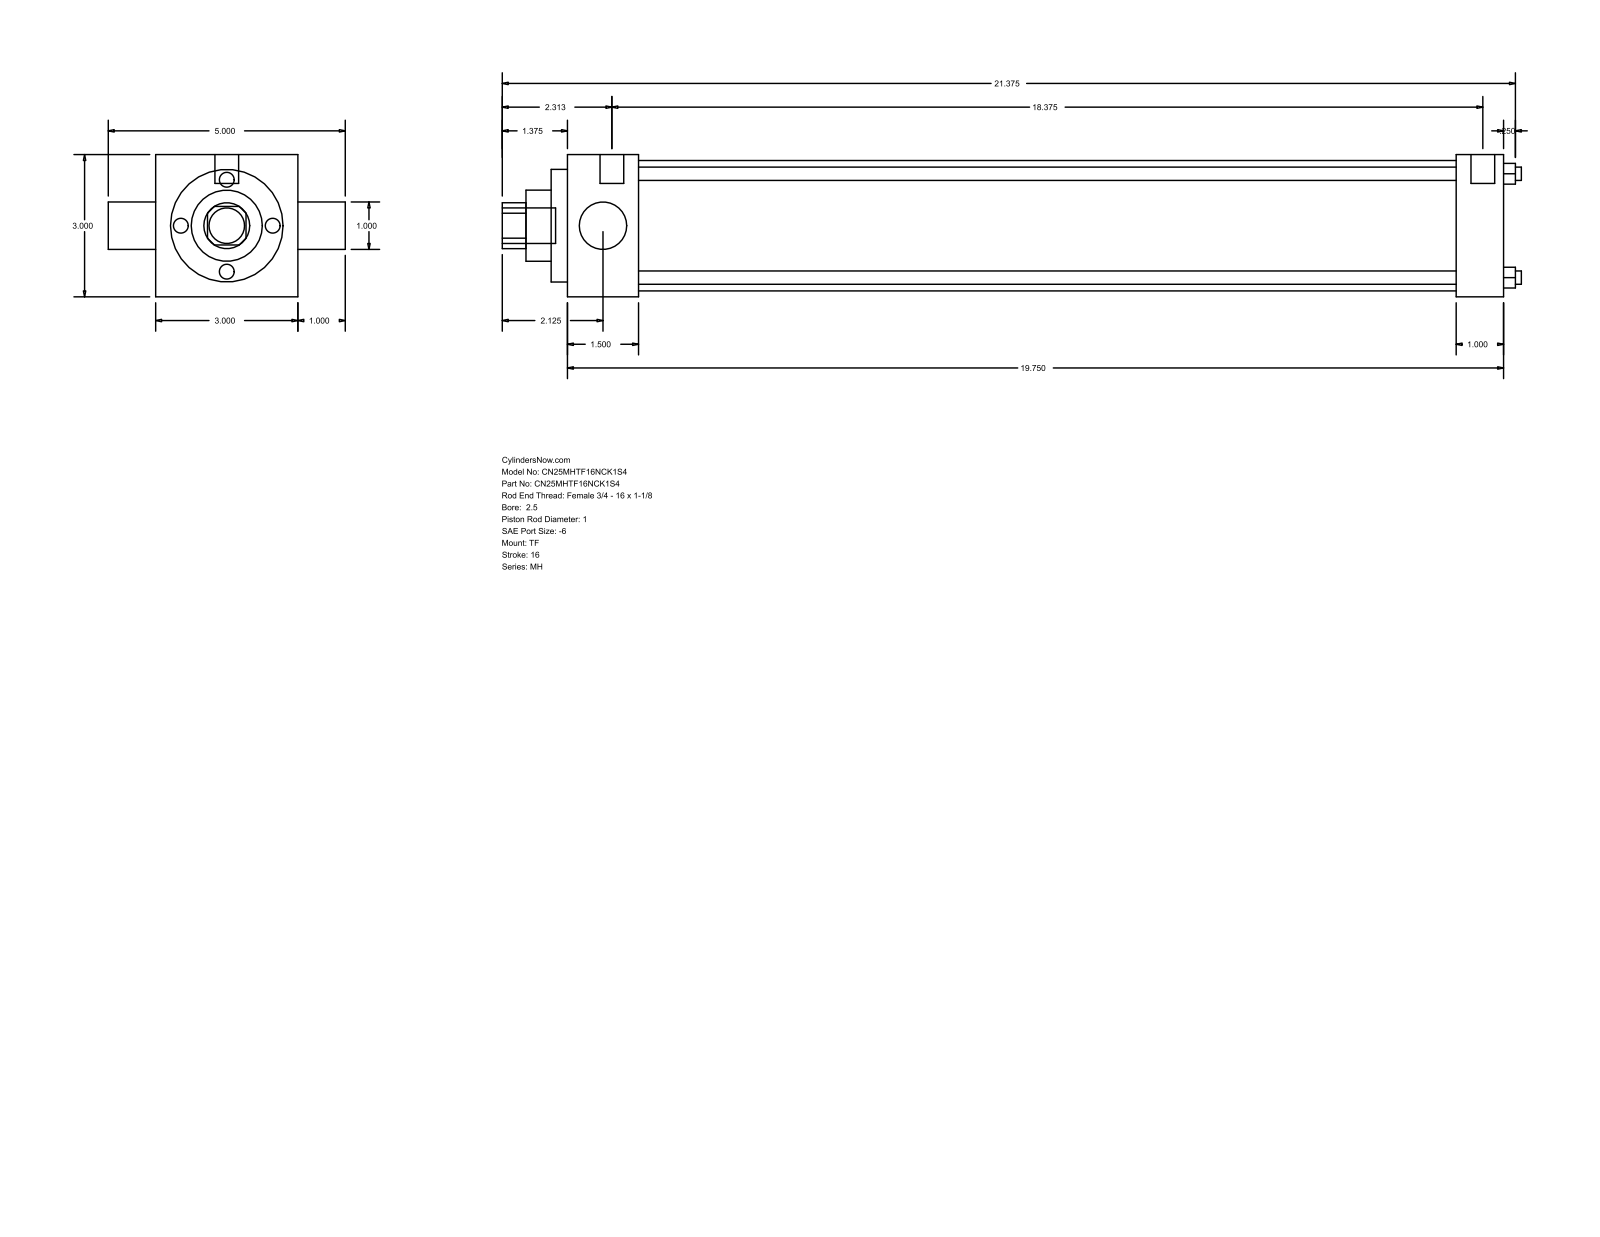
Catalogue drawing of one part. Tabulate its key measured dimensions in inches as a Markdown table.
| quantity | value |
| --- | --- |
| part name | MH_TF__0250_1 |
| STEP written by | GSSL Pune (CONFIG_CONTROL_DESIGN) |
| units | inches |
| bodies | 0 solids, 86 faces (61 planar, 25 cylindrical, 0 other) |
| overall size | 21.5 × 5 × 3 |
| round holes (diameter × count) | 0.281 × 4, 1 × 2, 1.5 × 1, 2.375 × 1, 2.75 × 1 |
| round bosses / shafts (diameter × count) | 0.219 × 3, 0.5 × 2, 0.75 × 1 |
| partial cylindrical surfaces (radius × count) | 0.484 × 1 |
| main face-to-face distances | 3, 19.75, 1, 1.5, 18.25, 18.75, 17.25, 0.344, 1.844, 19.094 |
| hole center spacings | 1.548, 2.19, 3.097 |
